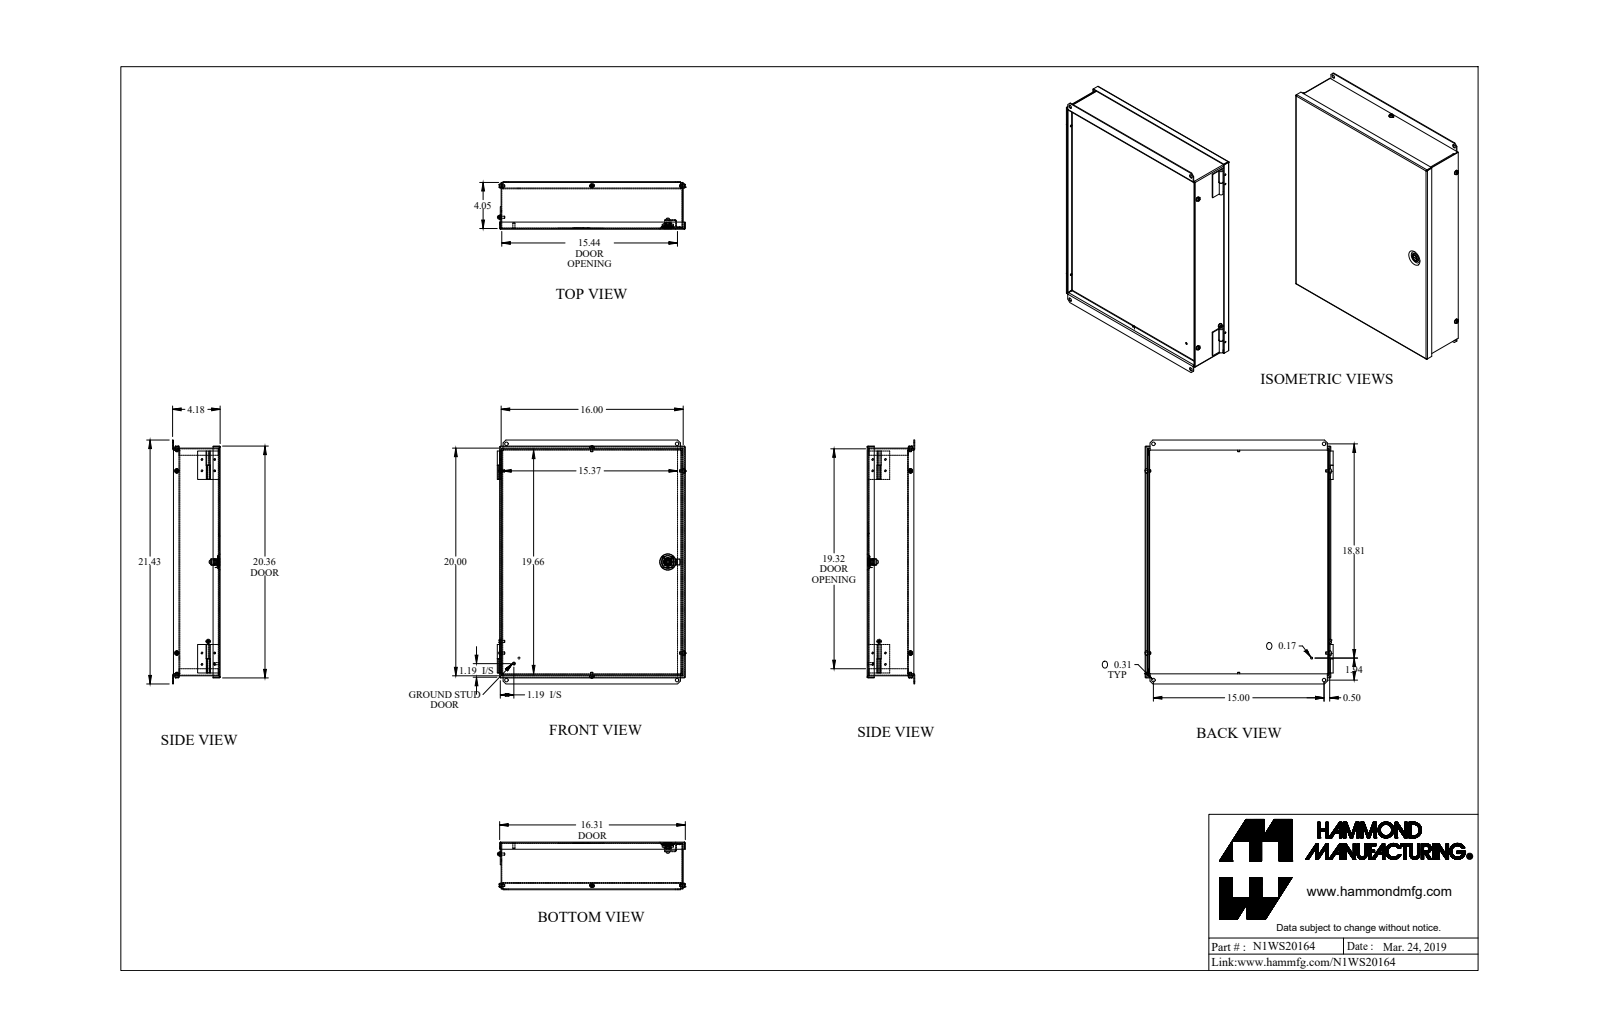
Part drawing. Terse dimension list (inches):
name: N1WS20164
written by: SolidWorks 2018 (AUTOMOTIVE_DESIGN)
unit: in
bodies: 17 solids, 607 faces (328 planar, 214 cylindrical, 65 other)
size: 21.425 × 16.519 × 4.179
volume: 66.4 in³; area: 2 141 in²
holes: 8× ⌀0.14, 5× ⌀0.17, 4× ⌀0.312, 1× ⌀0.187, 1× ⌀0.319, 1× ⌀0.476
bosses: 8× ⌀0.128, 4× ⌀0.19, 3× ⌀0.375, 1× ⌀0.787, 1× ⌀0.547, 1× ⌀0.472, 1× ⌀0.469, 1× ⌀0.375
rounds: 9× R0.029, 9× R0.086, 8× R0.036, 6× R0.108, 6× R0.109, 4× R0.012, 4× R0.1, 2× R0.079
face distances: 0.072, 0.057, 0.057, 3.564, 3.621, 3.492, 3.549, 15.943, 19.943, 15.886
hole spacings: 1, 1.119, 1.501, 17, 17.037, 16, 2.195, 2.412
